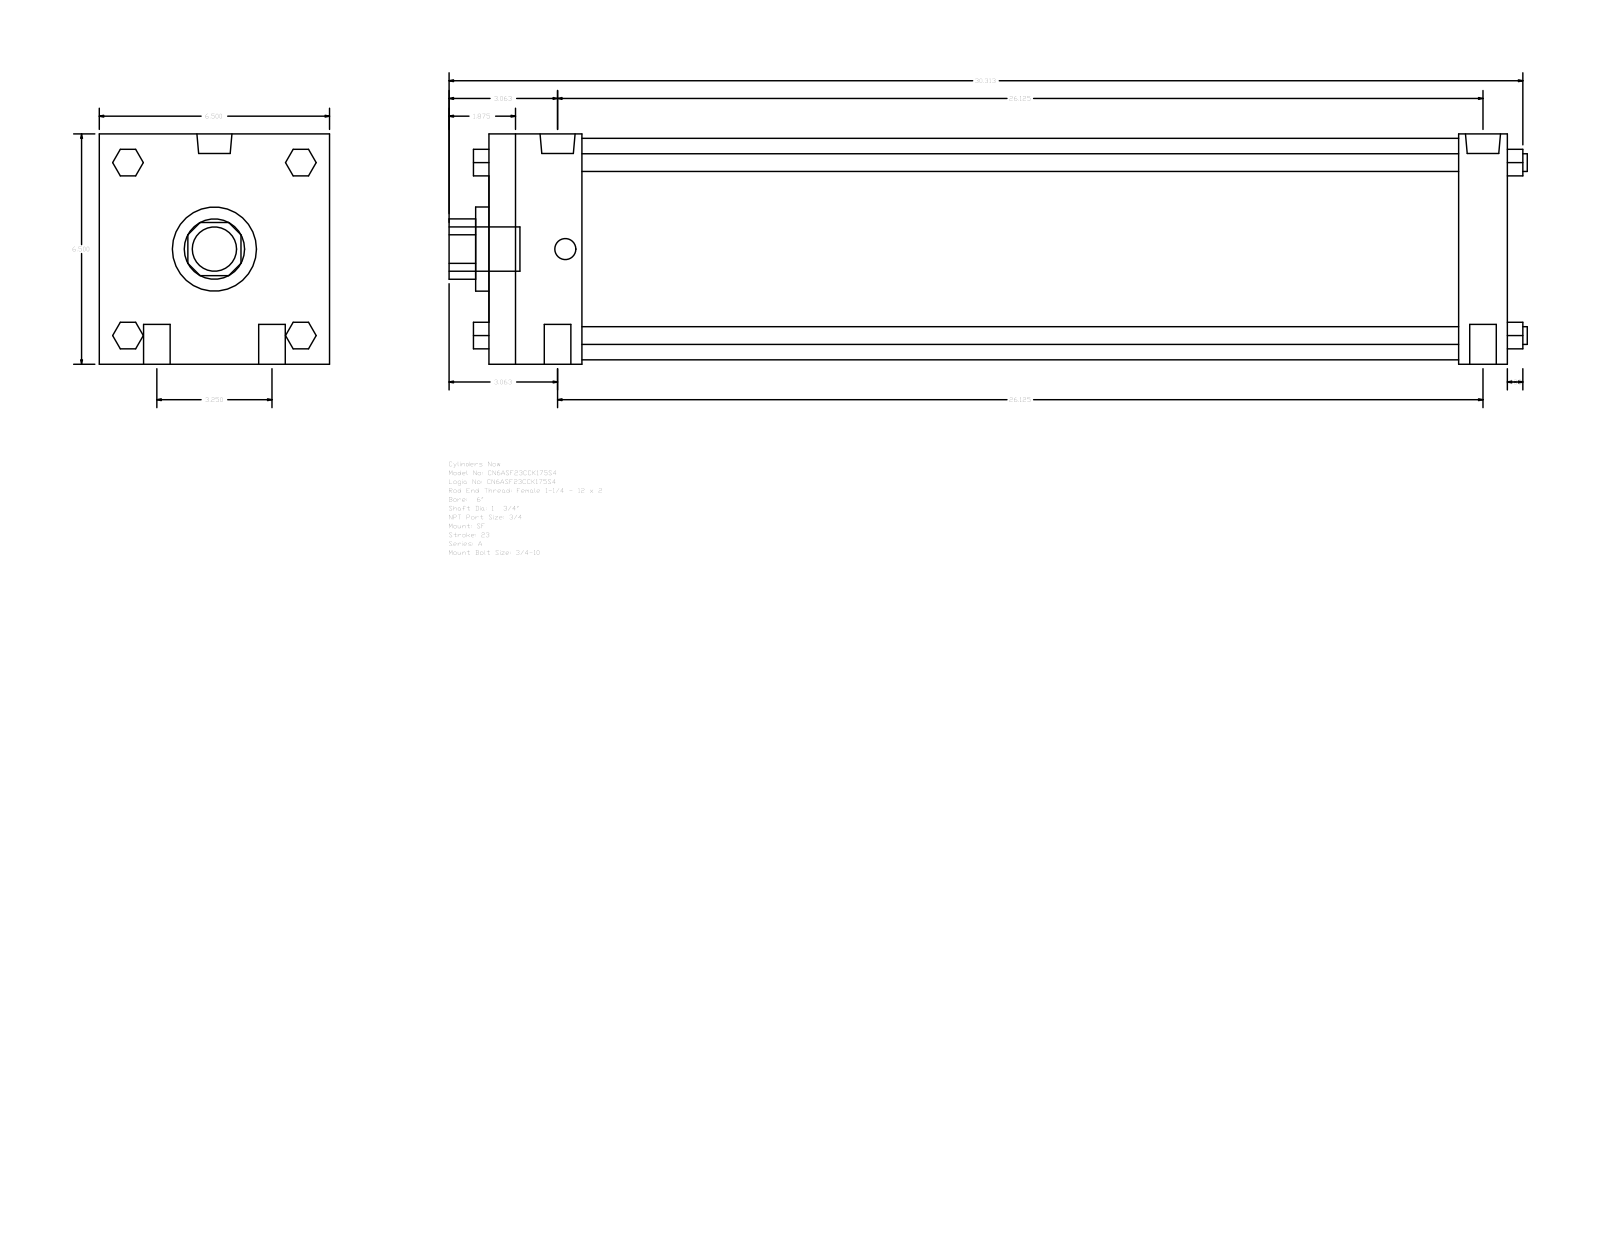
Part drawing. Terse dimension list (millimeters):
name: A_SF__0600_1.75
written by: GSSL Pune (CONFIG_CONTROL_DESIGN)
unit: mm
bodies: 0 solids, 124 faces (94 planar, 30 cylindrical, 0 other)
size: 773.11 × 165.1 × 165.1
holes: 1× ⌀44.45, 1× ⌀60.33, 1× ⌀158.75
bosses: 4× ⌀19.05, 4× ⌀12.7, 2× ⌀25.12, 2× ⌀15.08, 1× ⌀31.75
rounds: 1× R21.63
face distances: 165.1, 730.26, 695.33, 34.93, 66.68, 628.65, 663.58, 19.05, 61.97, 107.34
